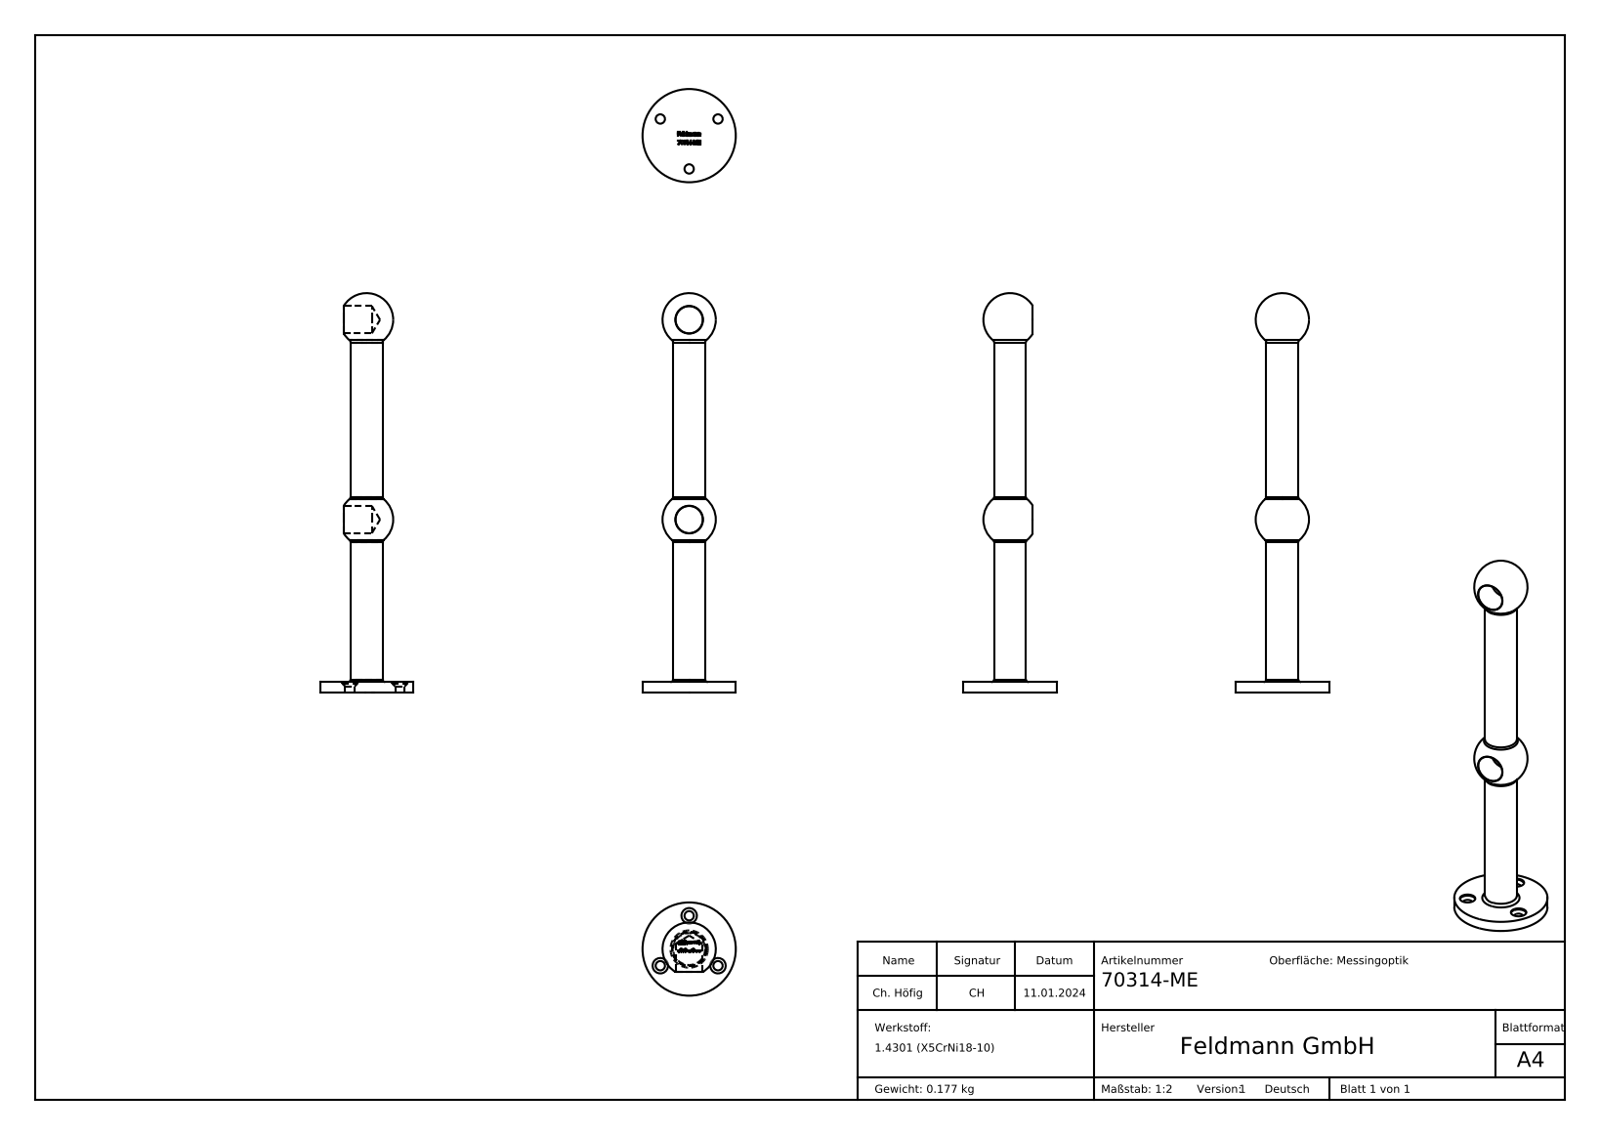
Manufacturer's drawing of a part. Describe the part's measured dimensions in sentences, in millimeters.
The part is named "70314-ME". Its 3-D file was written by "SolidWorks 2018 (CONFIG_CONTROL_DESIGN)". It is 1 solid with 237 faces: 118 planar, 11 cylindrical and 108 other. Overall it measures 150 by 35 by 35 millimeters. Its volume is 22 369 cubic millimeters and its surface area 9 353 square millimeters. Round holes: 3 of diameter 3.5, 3 of diameter 5.8, 2 of diameter 10.2. Round bosses or shafts: 1 of diameter 35, 1 of diameter 12. The main face-to-face distances are 4, 3.9, 2.97, 0.39, 1.4, 3.39, 3.19, 3.66, 4.09, 1.12. The hole center spacings are 21.65, 21.66, 75.
